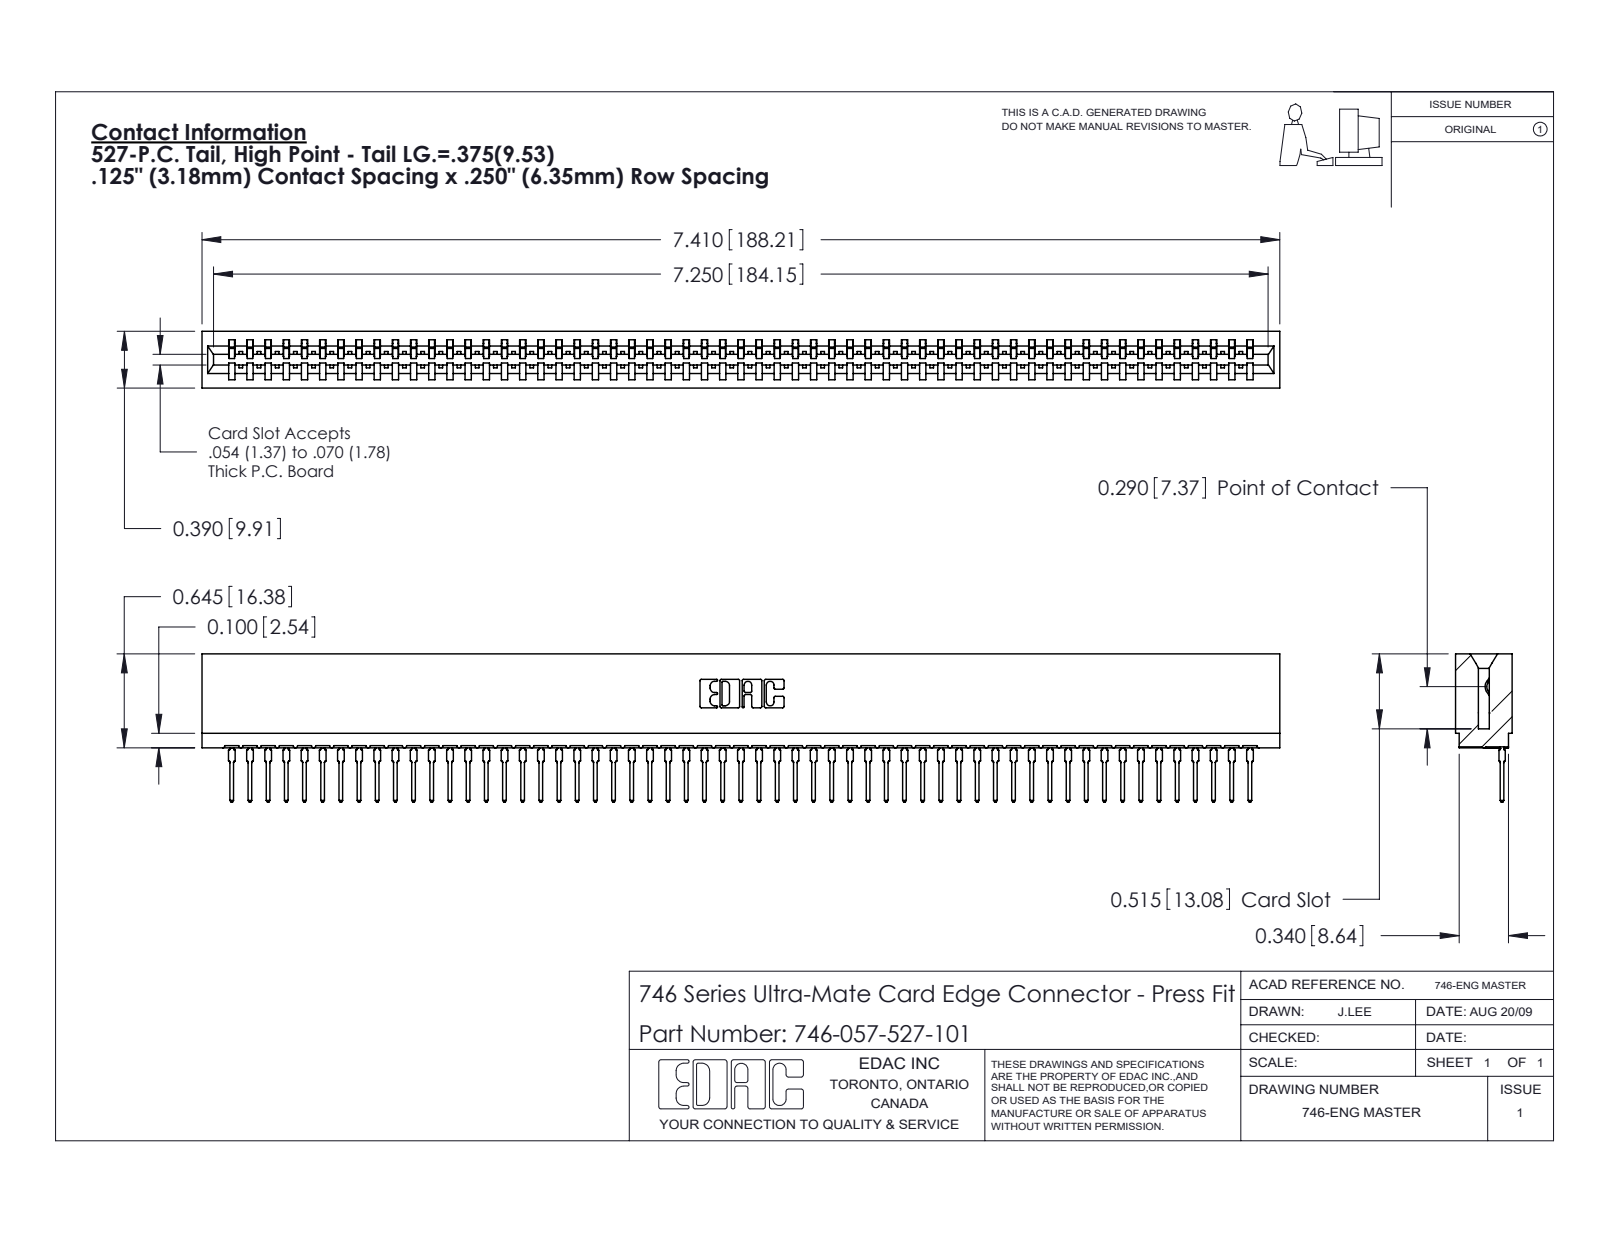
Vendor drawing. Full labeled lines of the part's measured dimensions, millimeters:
Part name (STEP PRODUCT): 746 Part_.515 Slot Depth - 01; 746-057-527-101; 746-292-001_527
STEP written by: SolidWorks 2020 (CONFIG_CONTROL_DESIGN)
Units: millimetres
Bodies: 58 solids, 6253 faces (3646 planar, 1125 cylindrical, 1482 other)
Overall size (bounding box): 188.2 × 25.9 × 9.9
Volume: 19 600 mm³ · Surface area: 29 660 mm²
Partial cylindrical surfaces — rounded edges, fillets, slot ends (radius × count): R0.5 ×114, R0.4 ×58, R0.3 ×22, R0.2 ×6, R0.8 ×6, R0.1 ×4, R0.3 ×4, R0.7 ×3
Main face-to-face distances: 1.4, 8.5, 9.9, 6.4, 0.6, 7.8, 7, 2.1, 4.4, 4
